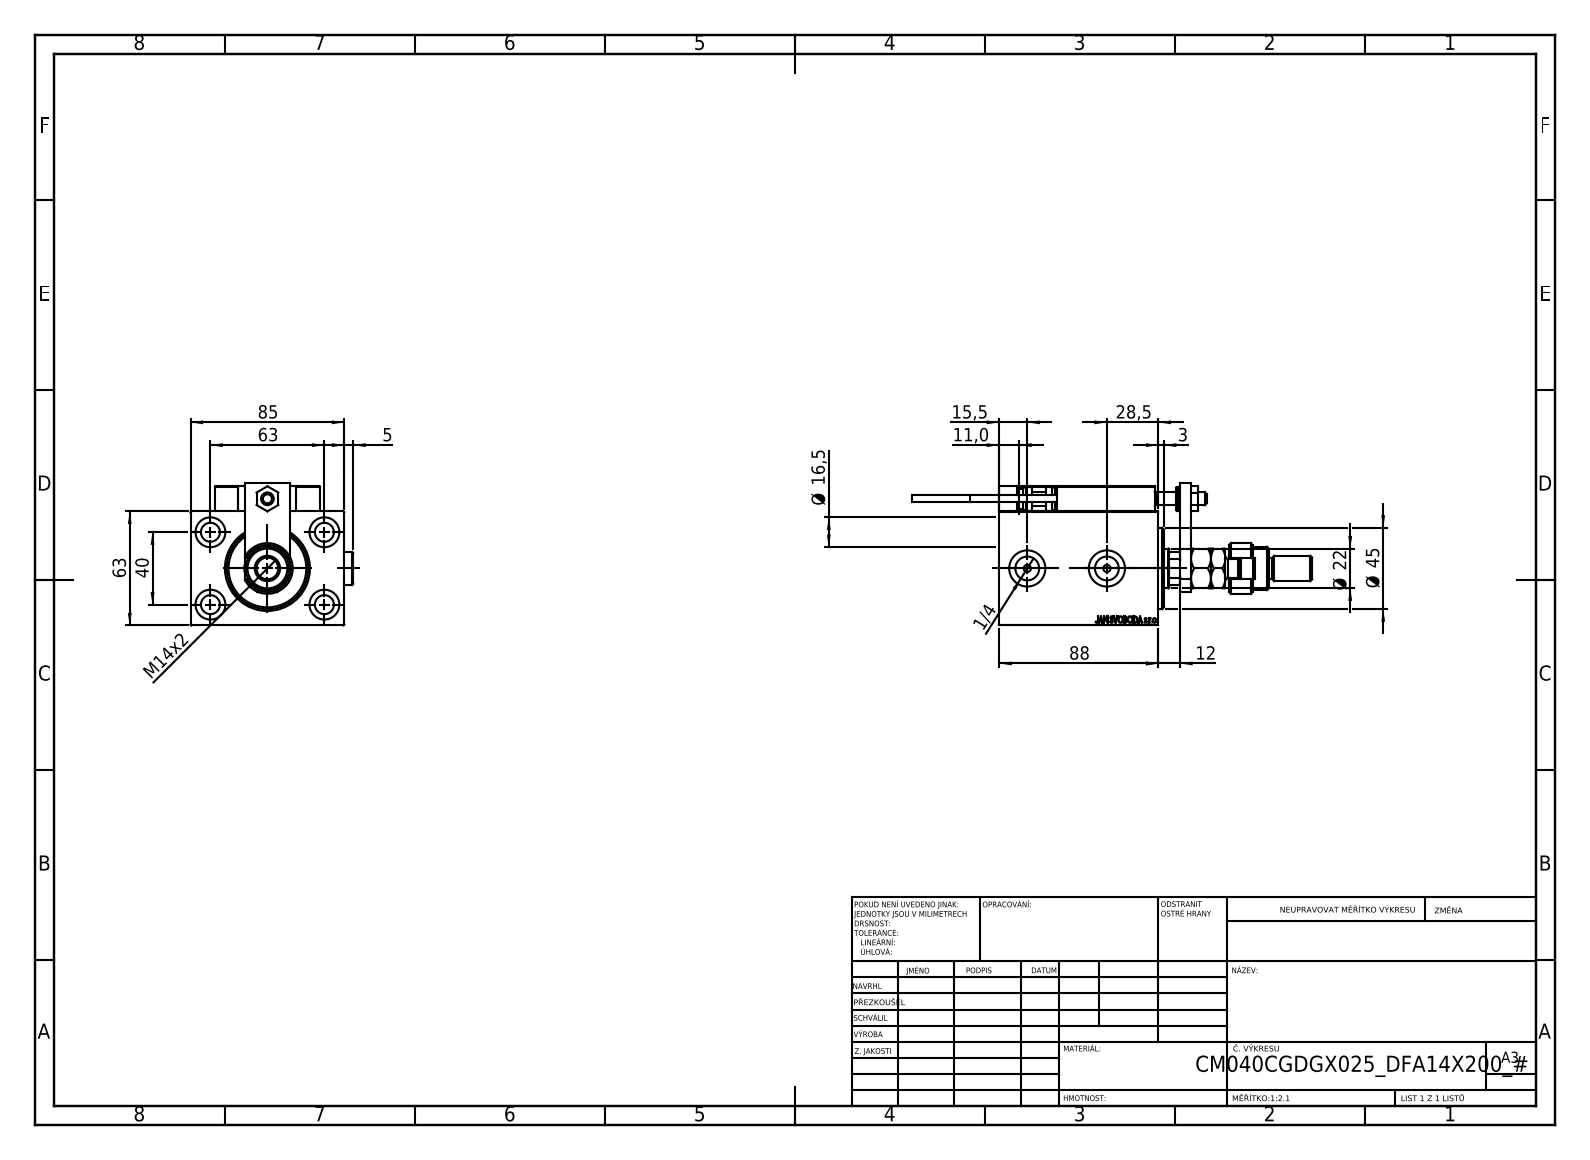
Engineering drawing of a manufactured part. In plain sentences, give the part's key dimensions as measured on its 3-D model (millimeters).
The part is named "MAGNET; ZARAZKA; KONCOVKA; X_Y_DFA (+8 more)". Its 3-D file was written by "SolidWorks 2019 (CONFIG_CONTROL_DESIGN)". It is 27 solids with 1421 faces: 622 planar, 217 cylindrical and 582 other. Overall it measures 221 by 89.9 by 78.5 millimeters. Its volume is 477 750 cubic millimeters and its surface area 112 757 square millimeters. Round holes: 6 of diameter 4, 5 of diameter 8, 5 of diameter 16.5, 4 of diameter 3.2, 4 of diameter 10.5, 2 of diameter 5, 2 of diameter 13.16, 2 of diameter 20, 1 of diameter 7, 1 of diameter 12.5, 1 of diameter 22, 1 of diameter 25.5. Round bosses or shafts: 3 of diameter 18, 2 of diameter 11, 2 of diameter 5, 2 of diameter 3.8, 1 of diameter 28, 1 of diameter 24, 1 of diameter 14, 1 of diameter 13. Partial cylindrical surfaces (rounded edges, fillets, slot ends): 30 of radius 0.3, 2 of radius 3, 1 of radius 9.75, 1 of radius 10.5. The main face-to-face distances are 63, 12, 76, 85, 88, 14, 77, 25, 30, 18. The hole center spacings are 37.31, 11.37, 20, 29.59, 29.69, 36.06, 36.53, 40.
